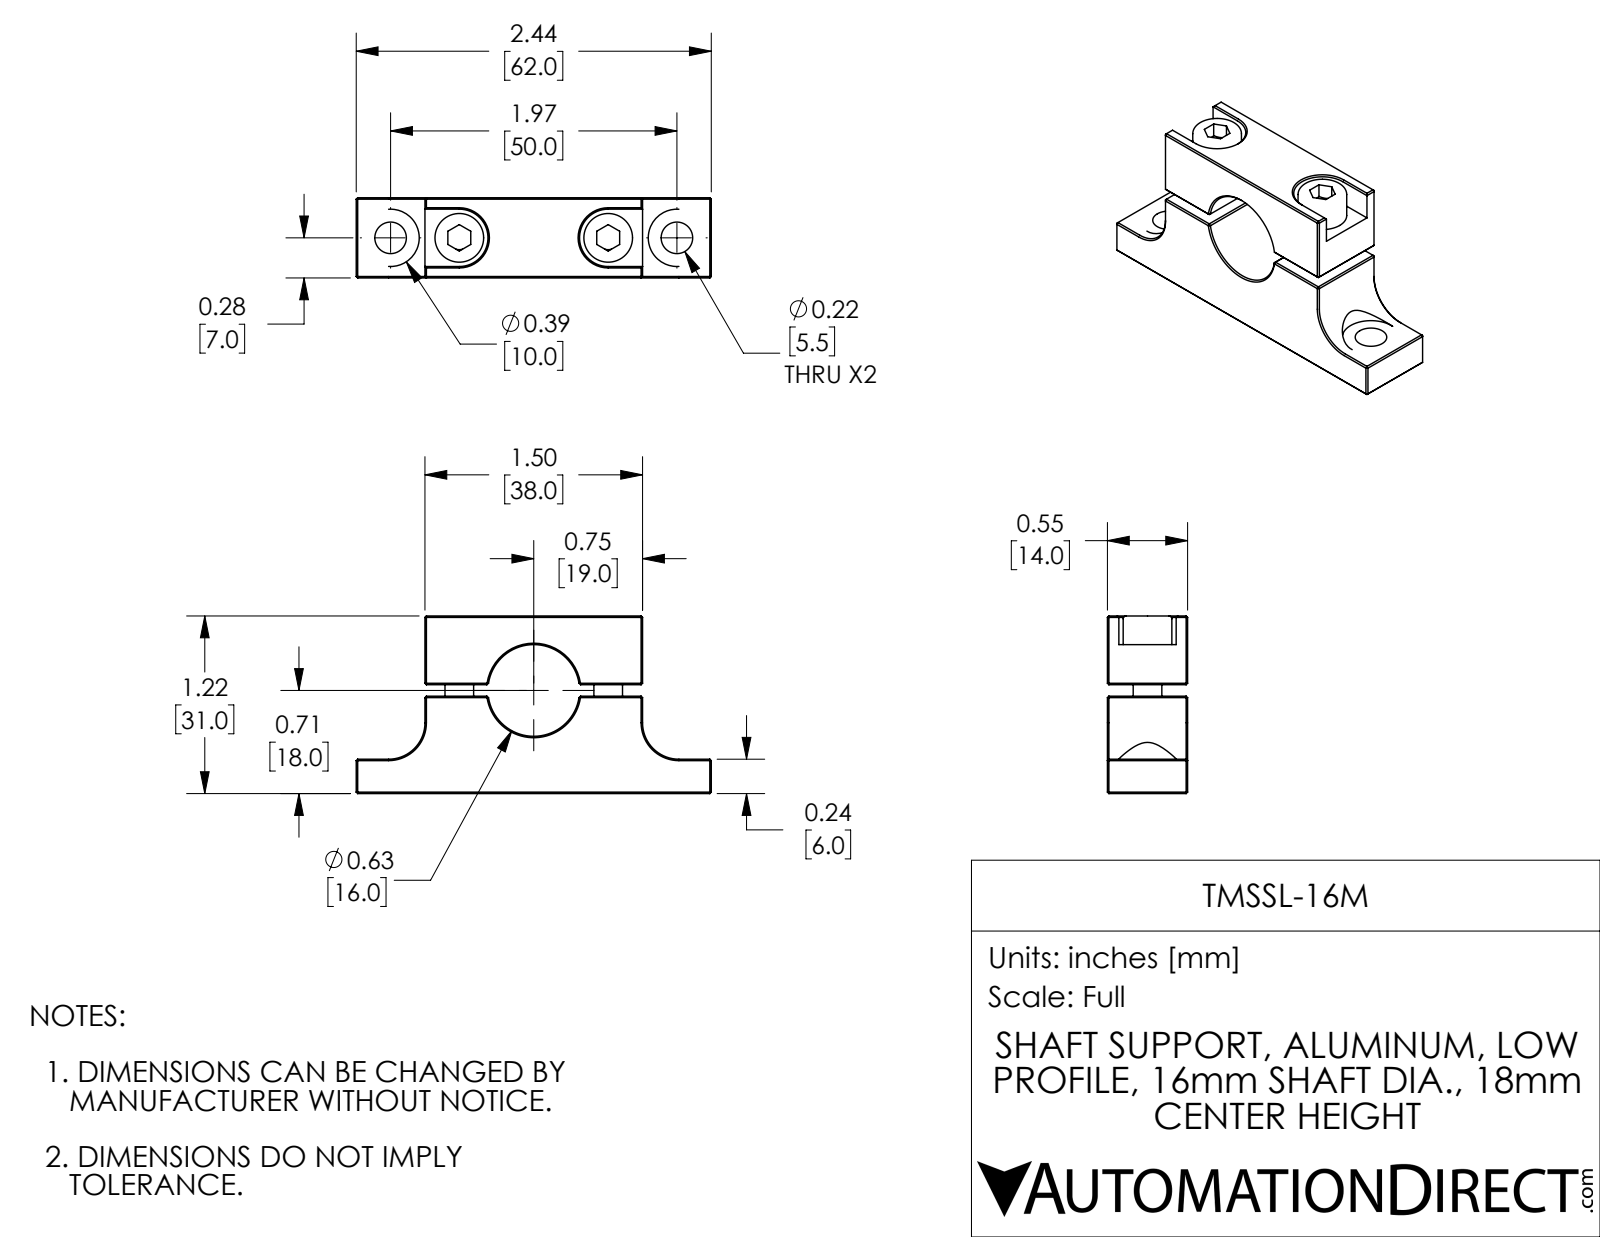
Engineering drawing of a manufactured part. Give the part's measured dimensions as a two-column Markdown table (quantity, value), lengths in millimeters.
| quantity | value |
| --- | --- |
| part name | TMSSL-16M |
| STEP written by | SolidWorks 2017 (AUTOMOTIVE_DESIGN) |
| units | millimeters |
| bodies | 4 solids, 179 faces (118 planar, 32 cylindrical, 29 other) |
| overall size | 62 × 31 × 14 |
| volume | 14 300 mm³ |
| surface area | 7 735 mm² |
| round holes (diameter × count) | 5.5 × 4, 4.1 × 2, 2.4 × 1, 16 × 1 |
| round bosses / shafts (diameter × count) | 8.5 × 2, 5 × 2 |
| partial cylindrical surfaces (radius × count) | 5 × 4, 6.4 × 2 |
| main face-to-face distances | 14, 12, 31, 2, 17, 9, 7, 19, 26, 5 |
| hole center spacings | 12, 13, 25, 38, 26, 50 |
